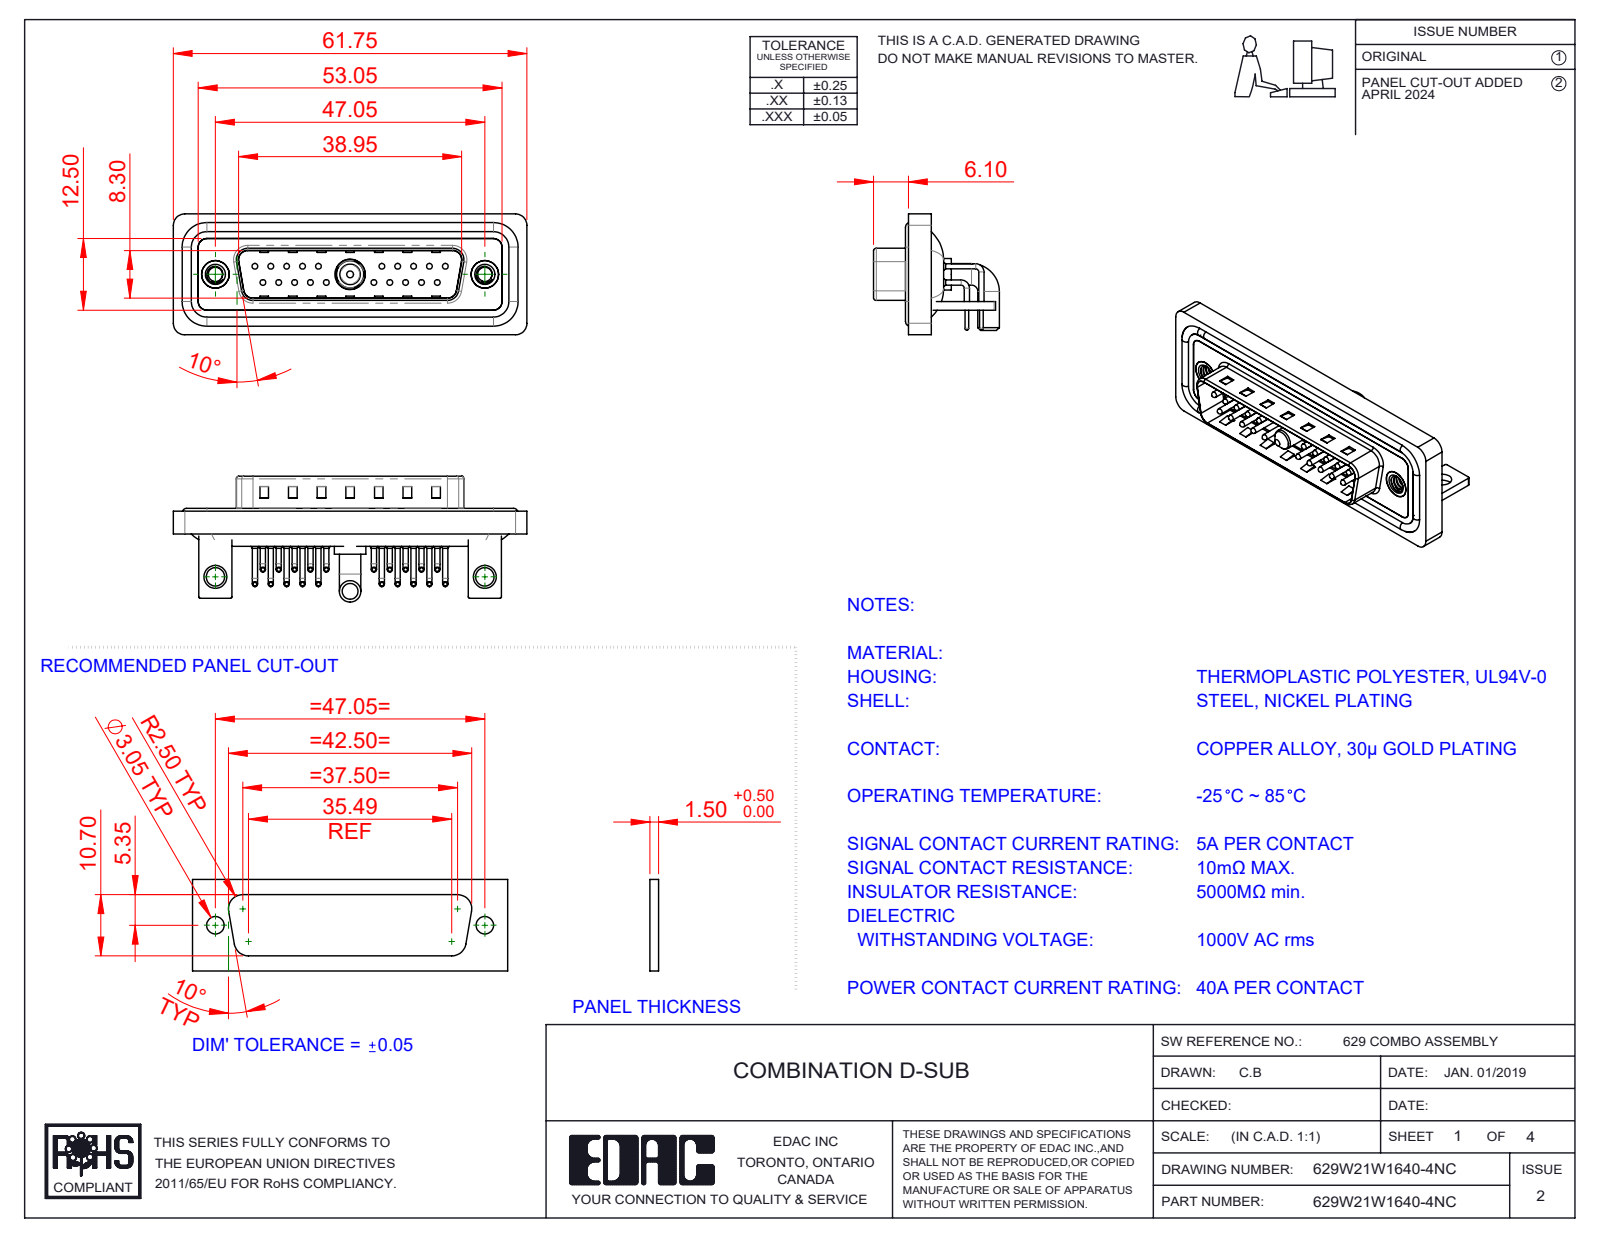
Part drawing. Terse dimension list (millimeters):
name: 629Combo Shell Rear_25 Contacts; Power Pin_40A RA; 629Combo Housing_21W1; 629Combo Contact Row 1 (+6 more)
written by: SolidWorks 2023 (CONFIG_CONTROL_DESIGN)
unit: mm
bodies: 31 solids, 2764 faces (1519 planar, 947 cylindrical, 298 other)
size: 61.75 × 21.98 × 21.1
volume: 7 763 mm³; area: 13 353 mm²
holes: 20× ⌀0.75, 20× ⌀1.6, 20× ⌀2, 2× ⌀2.5, 2× ⌀3.2, 2× ⌀4, 2× ⌀4.8, 2× ⌀5, 1× ⌀4.85, 1× ⌀5.3
bosses: 40× ⌀0.9, 20× ⌀1.5, 20× ⌀1, 20× ⌀0.65, 4× ⌀1.6, 2× ⌀4.9, 2× ⌀3.75, 1× ⌀5.5
rounds: 20× R1.01, 19× R2, 18× R1.5, 16× R0.25, 9× R0.5, 8× R1.6, 4× R0.6, 4× R0.65
face distances: 0.4, 0.8, 2.1, 2.9, 1.5, 1.1, 4.1, 1.6, 4.5, 3.7
hole spacings: 3.16, 2.77, 5.54, 8.31, 5.04, 19.39, 20.97, 22.16
